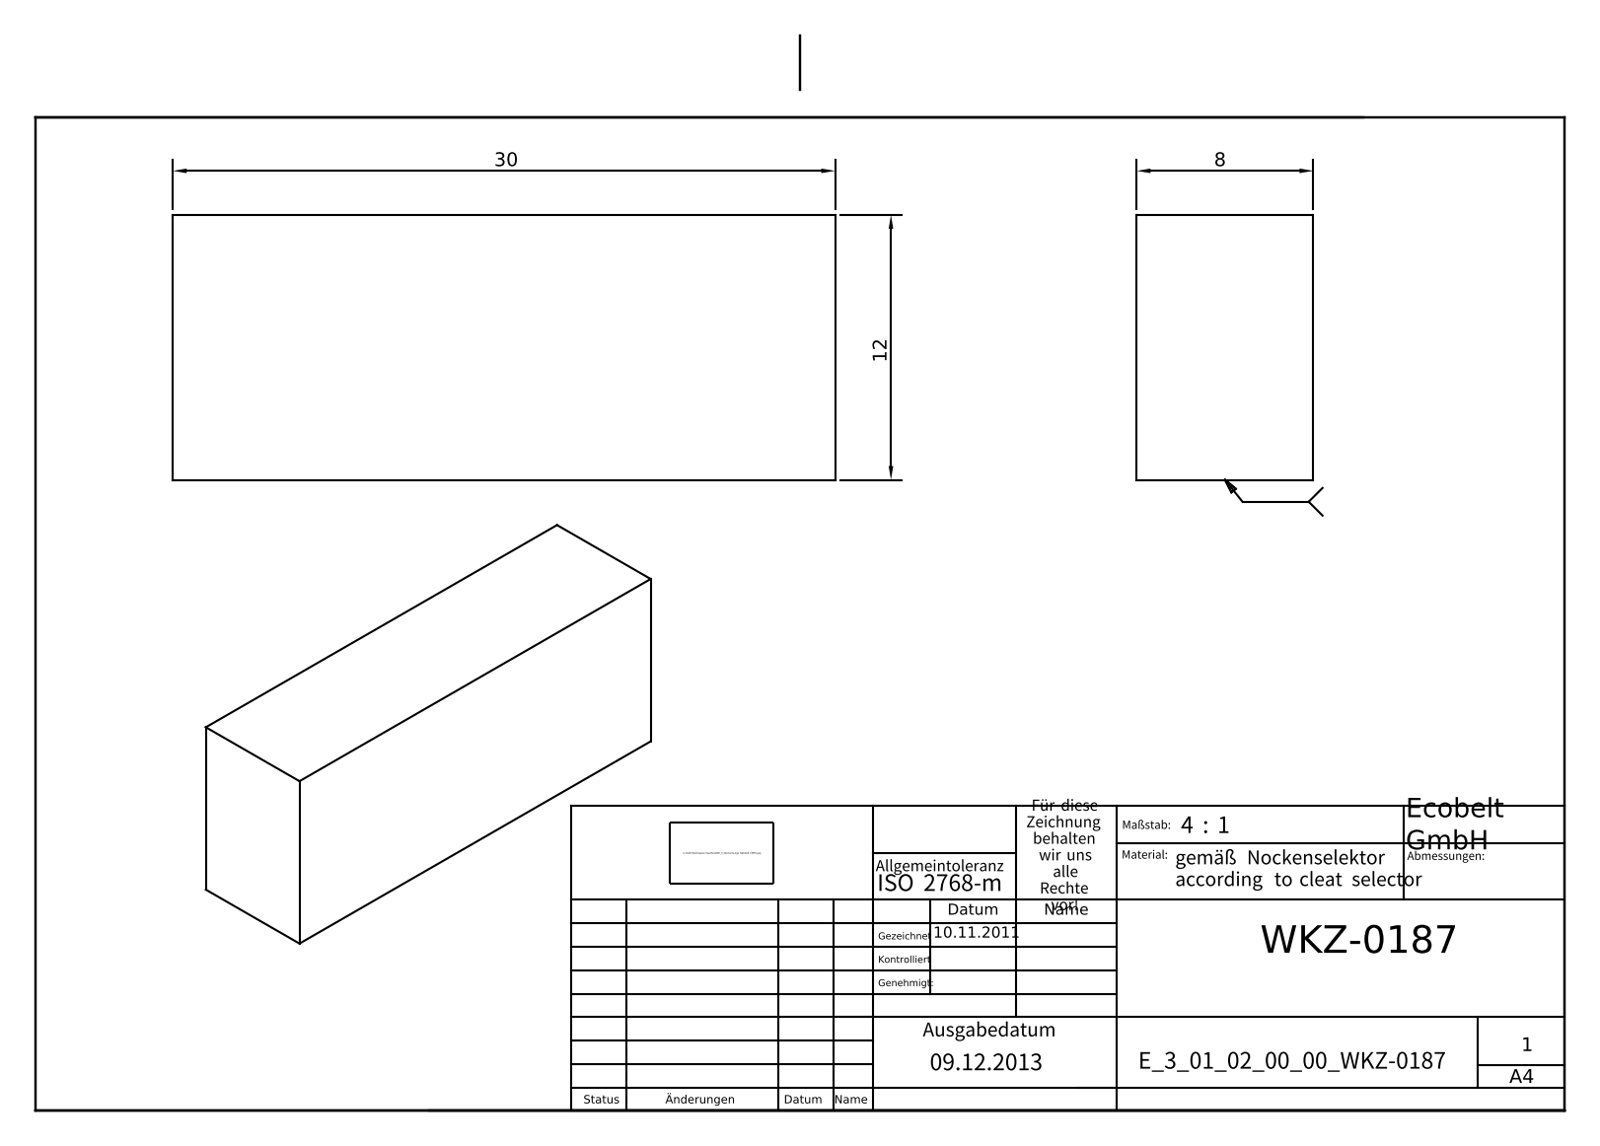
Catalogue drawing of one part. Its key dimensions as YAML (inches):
part_name: "E_3_01_02_00_00_WKZ-0187"
step_written_by: "Autodesk Inventor 2021 (AUTOMOTIVE_DESIGN)"
units: inches
bodies: {solids: 1, faces: 6, planar: 6, cylindrical: 0, other: 0}
overall_size: [1.181, 0.472, 0.315]
volume: 0.176
surface_area: 2.158
face_to_face_distances: [0.315, 0.472, 1.181]
